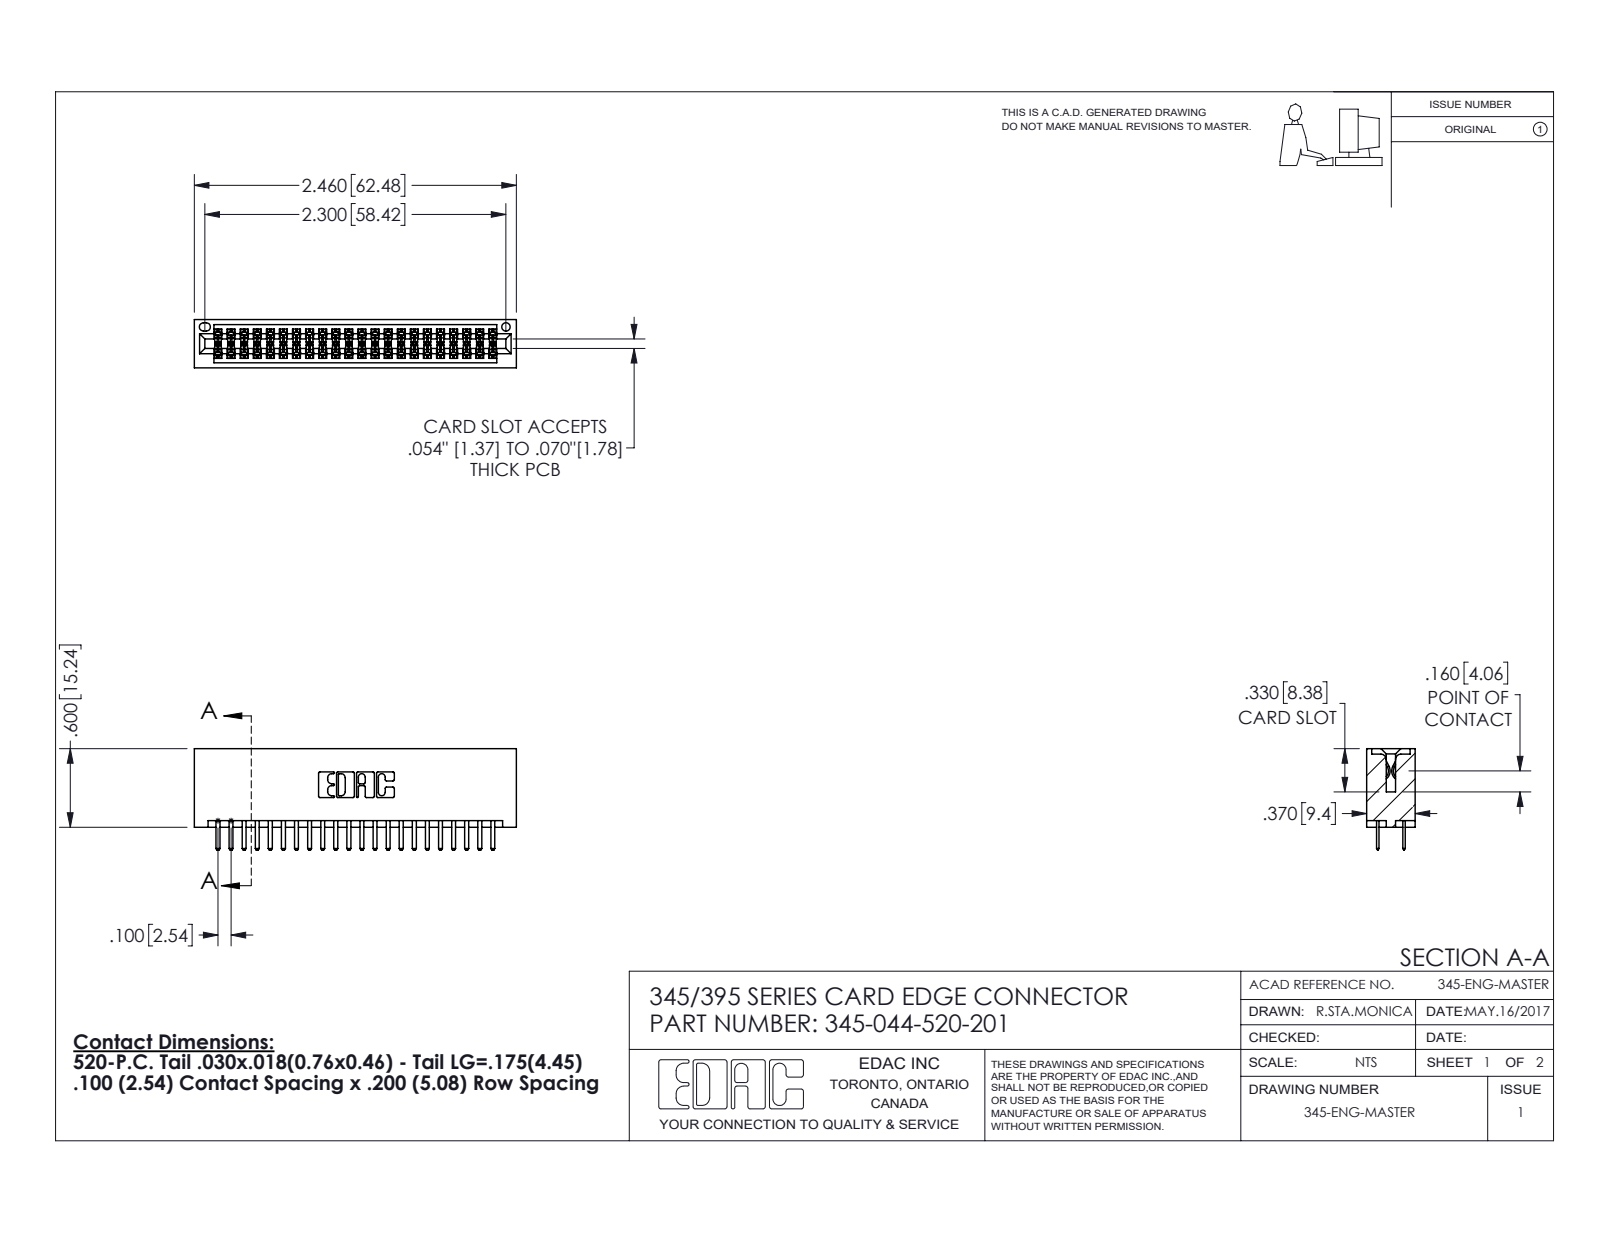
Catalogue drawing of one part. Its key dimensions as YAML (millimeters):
part_name: "345-292-001_345-293-120; 345 Part_No Mounting Lugs; 345-044-520-201"
step_written_by: "SolidWorks 2016 (CONFIG_CONTROL_DESIGN)"
units: millimeters
bodies: {solids: 45, faces: 2494, planar: 1616, cylindrical: 878, other: 0}
overall_size: [62.5, 19.7, 9.4]
volume: 6470
surface_area: 9452
round_holes:
  - {diameter: 1.6, count: 1}
partial_cylinders:
  - {radius: 0.2, count: 66}
  - {radius: 0.3, count: 48}
  - {radius: 0.3, count: 22}
  - {radius: 0.2, count: 6}
  - {radius: 0.8, count: 6}
  - {radius: 0.7, count: 3}
  - {radius: 0.4, count: 2}
  - {radius: 0.5, count: 2}
face_to_face_distances: [7.6, 1.8, 5.1, 9.4, 2.5, 6.9, 0.6, 5.7, 0.6, 1.8]
